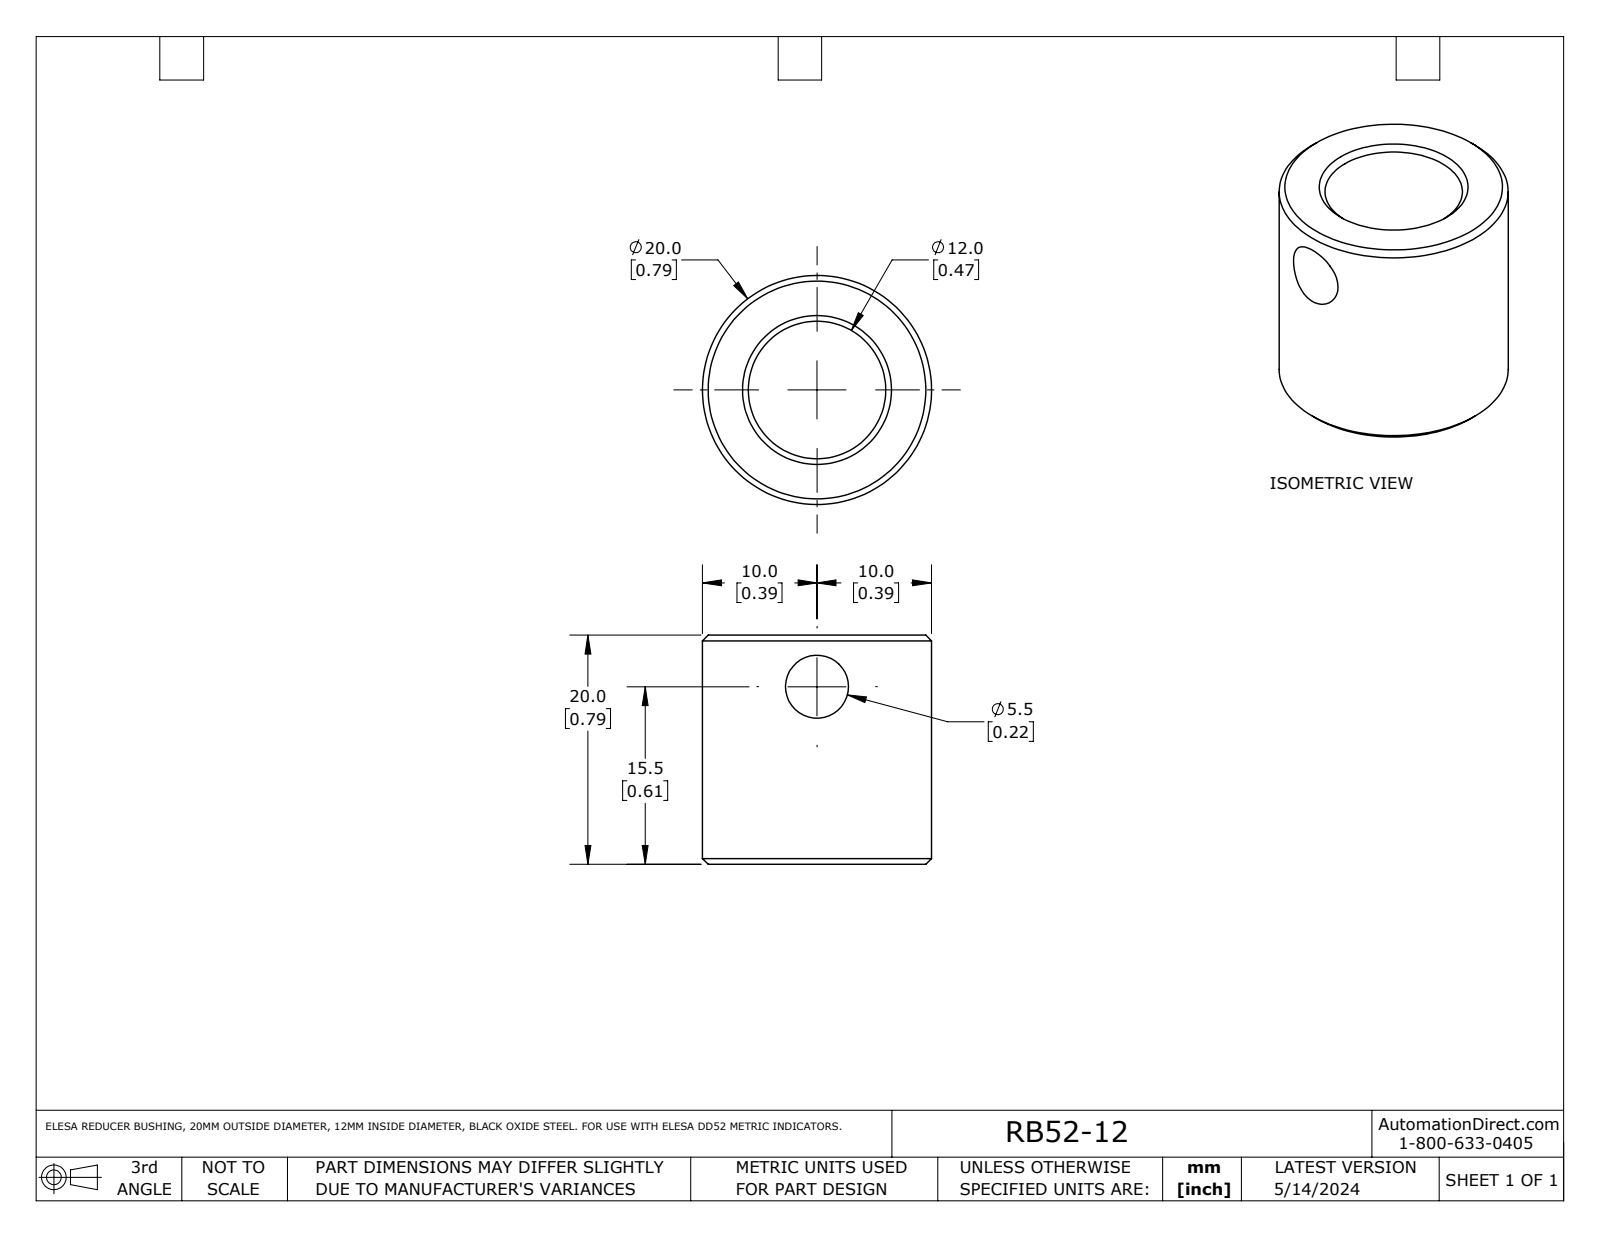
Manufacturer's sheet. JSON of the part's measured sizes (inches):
{"part_name": "RB52-12", "step_written_by": "SolidWorks 2023 (AUTOMOTIVE_DESIGN)", "units": "inches", "bodies": {"solids": 1, "faces": 9, "planar": 2, "cylindrical": 3, "other": 4}, "overall_size": [0.787, 0.787, 0.787], "volume_in3": 0.238, "surface_area_in2": 3.684, "round_holes": [[0.217, 1], [0.472, 1]], "round_bosses_or_shafts": [[0.787, 1]], "face_to_face_distances": [0.787]}
